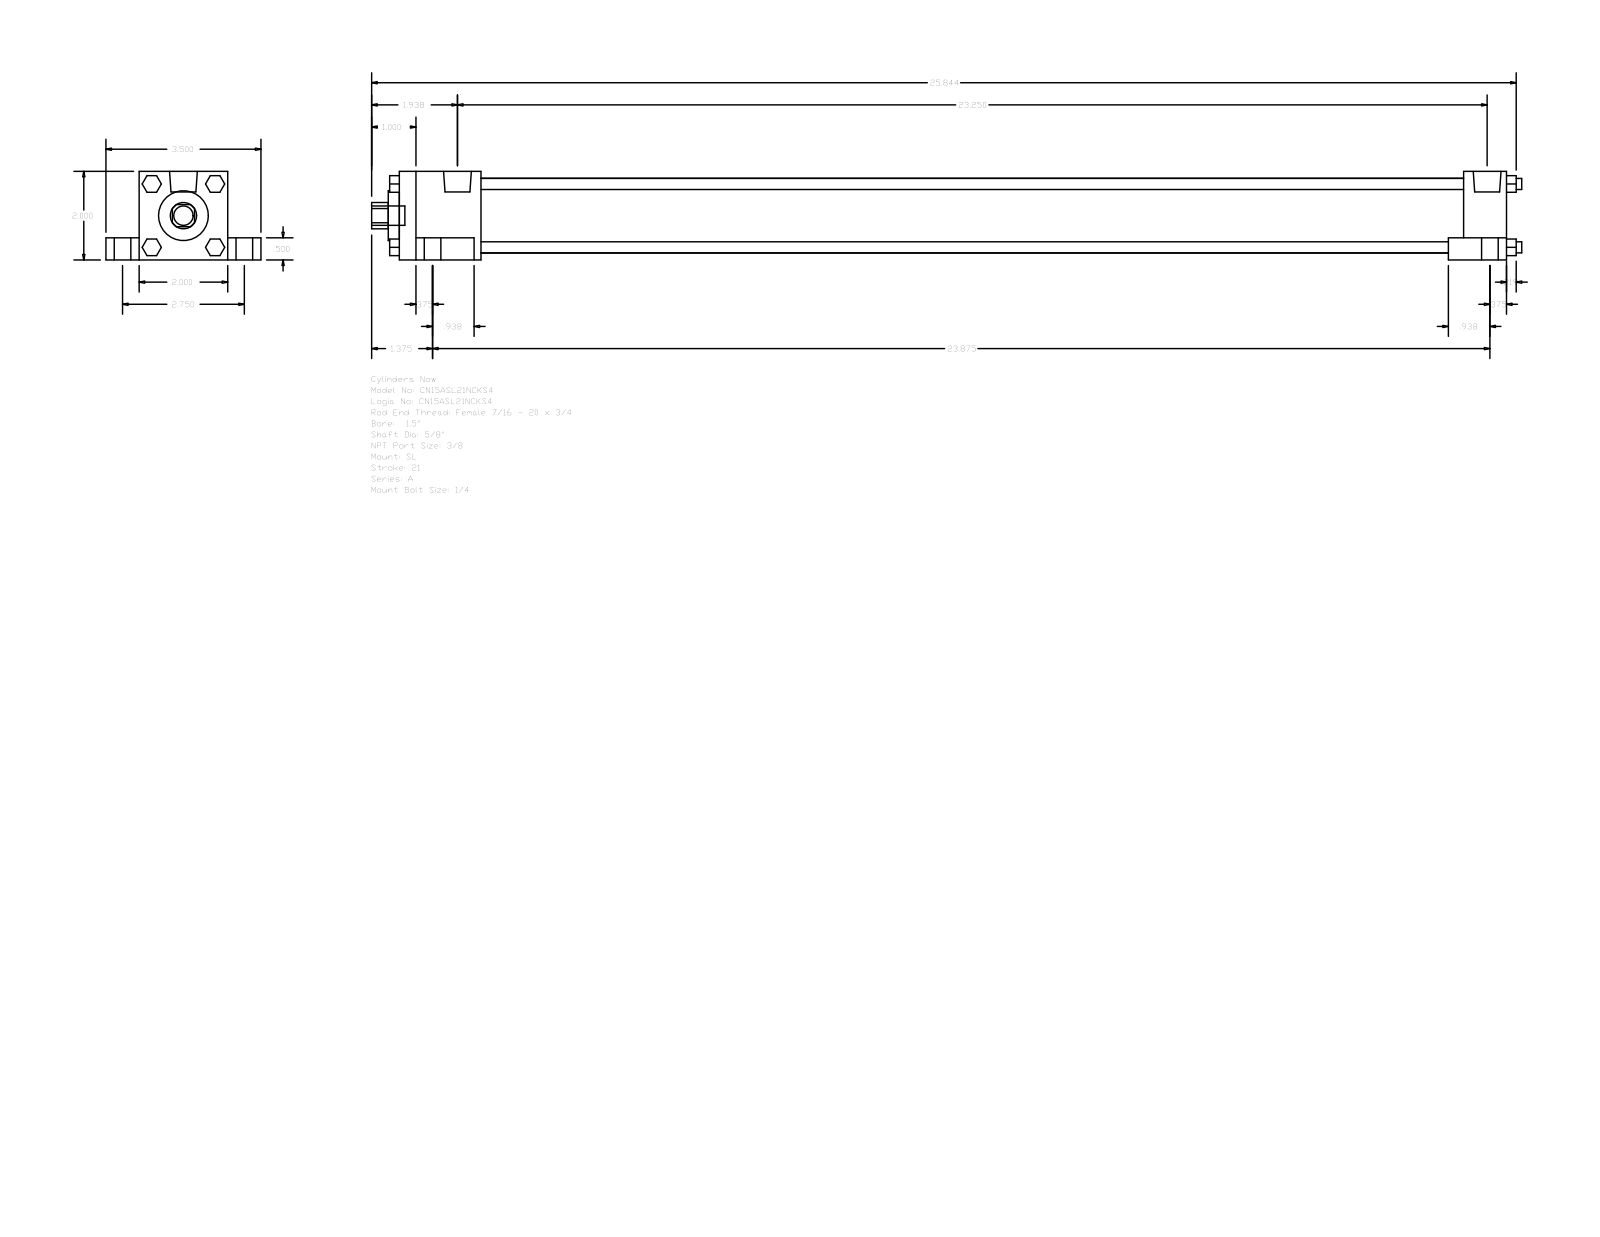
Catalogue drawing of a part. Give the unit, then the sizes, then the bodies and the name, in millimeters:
Units: millimetres
Overall size (bounding box): 659.61 × 88.9 × 50.8
Round holes (diameter × count): ⌀15.88 ×1, ⌀28.57 ×1, ⌀42.93 ×1
Round bosses / shafts (diameter × count): ⌀15.88 ×4, ⌀9.53 ×4, ⌀6.35 ×4, ⌀5.56 ×4, ⌀15.93 ×2, ⌀11.11 ×1
Partial cylindrical surfaces — rounded edges, fillets, slot ends (radius × count): R7.54 ×1
Main face-to-face distances: 50.8, 19.05, 12.7, 38.1, 69.85, 635, 9.52, 33.34, 610.39, 24.61
Bodies: 0 solids, 148 faces (112 planar, 36 cylindrical, 0 other)
Part name (STEP PRODUCT): A_SL__0150_0.625
STEP written by: GSSL Pune (CONFIG_CONTROL_DESIGN)
